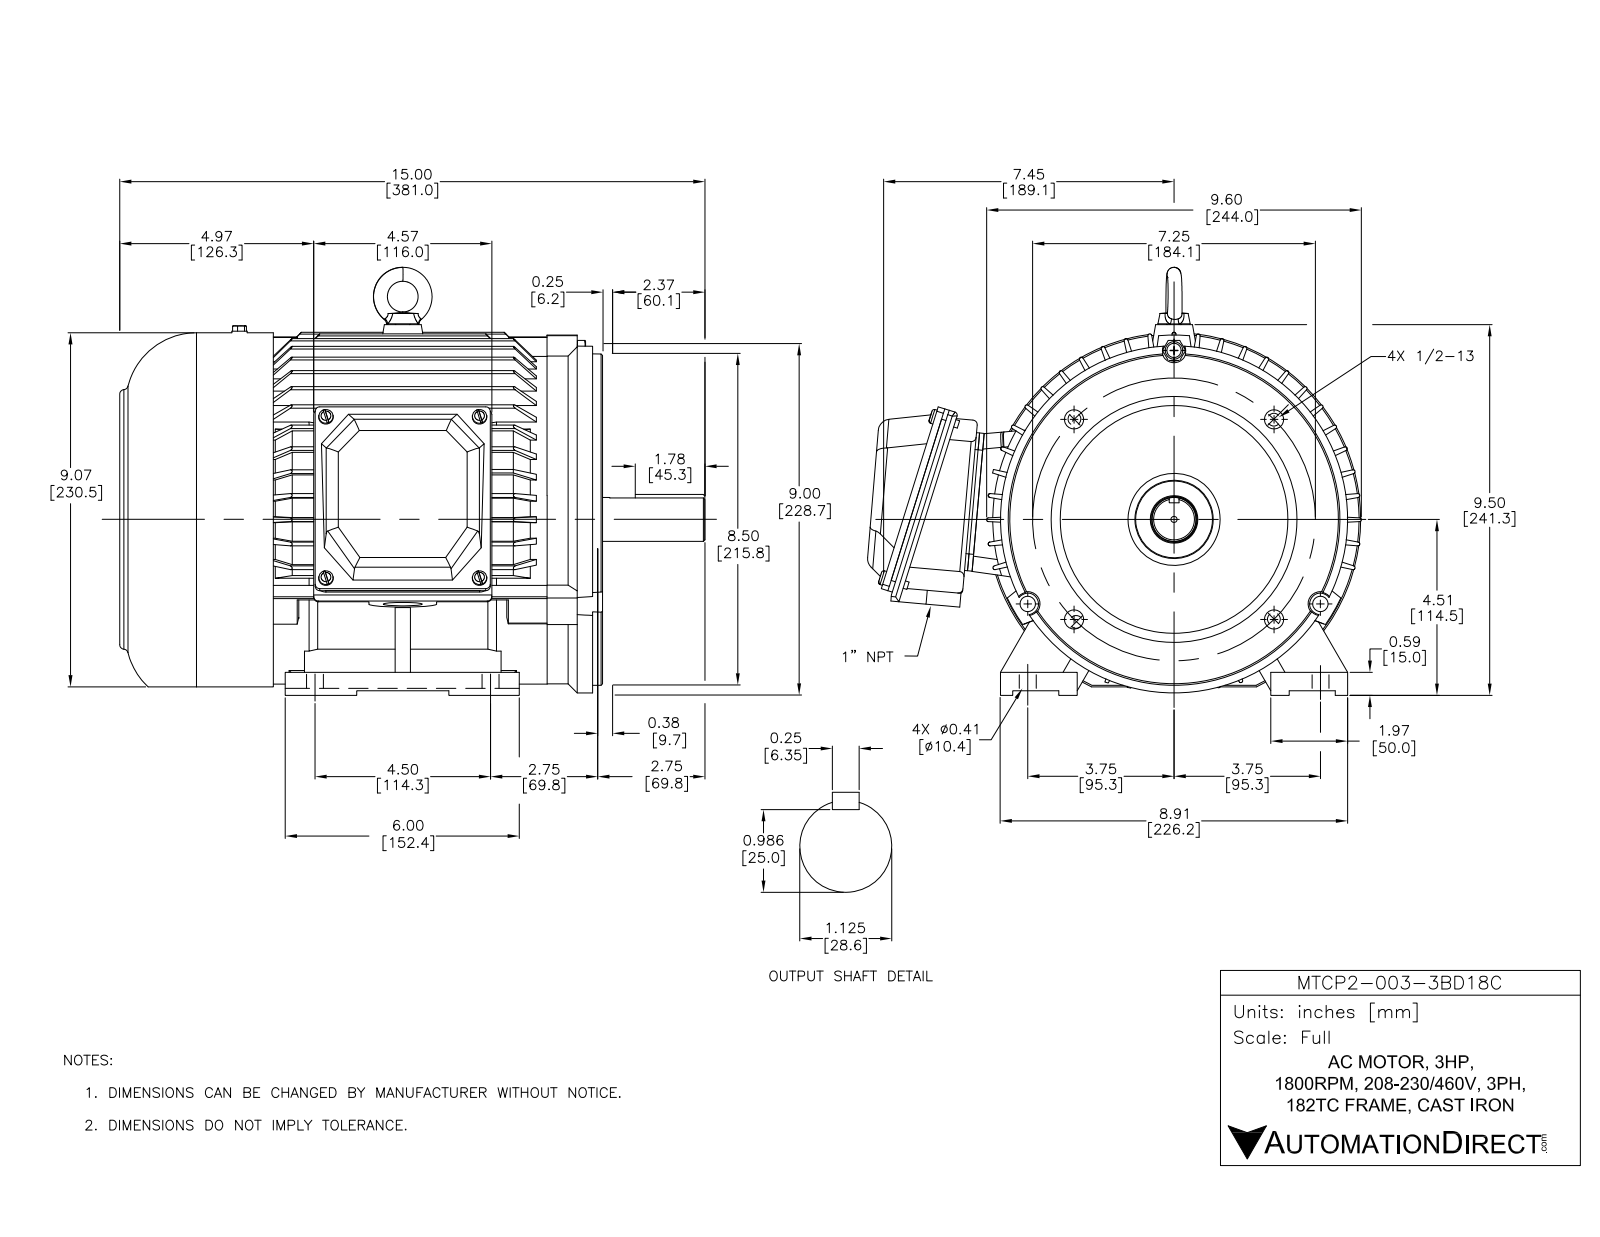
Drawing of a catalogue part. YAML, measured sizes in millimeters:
part_name: "PEWWE-182TC"
step_written_by: "SolidWorks 2017 (AUTOMOTIVE_DESIGN)"
units: millimeters
bodies: {solids: 16, faces: 1613, planar: 740, cylindrical: 567, other: 306}
overall_size: [381, 321.5, 278.6]
volume: 9124000
surface_area: 813500
round_holes:
  - {diameter: 5.8, count: 8}
  - {diameter: 7, count: 6}
  - {diameter: 5, count: 4}
  - {diameter: 6, count: 4}
  - {diameter: 11, count: 4}
  - {diameter: 12.5, count: 4}
  - {diameter: 10, count: 3}
  - {diameter: 8, count: 1}
  - {diameter: 9.2, count: 1}
  - {diameter: 25.4, count: 1}
  - {diameter: 30, count: 1}
  - {diameter: 50, count: 1}
round_bosses_or_shafts:
  - {diameter: 5, count: 4}
  - {diameter: 8, count: 2}
  - {diameter: 243, count: 1}
  - {diameter: 225.9, count: 1}
  - {diameter: 215.9, count: 1}
  - {diameter: 214, count: 1}
  - {diameter: 60, count: 1}
  - {diameter: 38, count: 1}
partial_cylinders:
  - {radius: 0.5, count: 256}
  - {radius: 3, count: 14}
  - {radius: 1.2, count: 9}
  - {radius: 1.5, count: 8}
  - {radius: 4, count: 8}
  - {radius: 7, count: 8}
  - {radius: 8, count: 8}
  - {radius: 2.3, count: 6}
face_to_face_distances: [1, 87.8, 3, 224.1, 311.9, 312.9, 88.8, 12, 0.5, 4]
hole_center_spacings: [100, 68, 96.2, 110, 110, 148.7, 110, 68]
